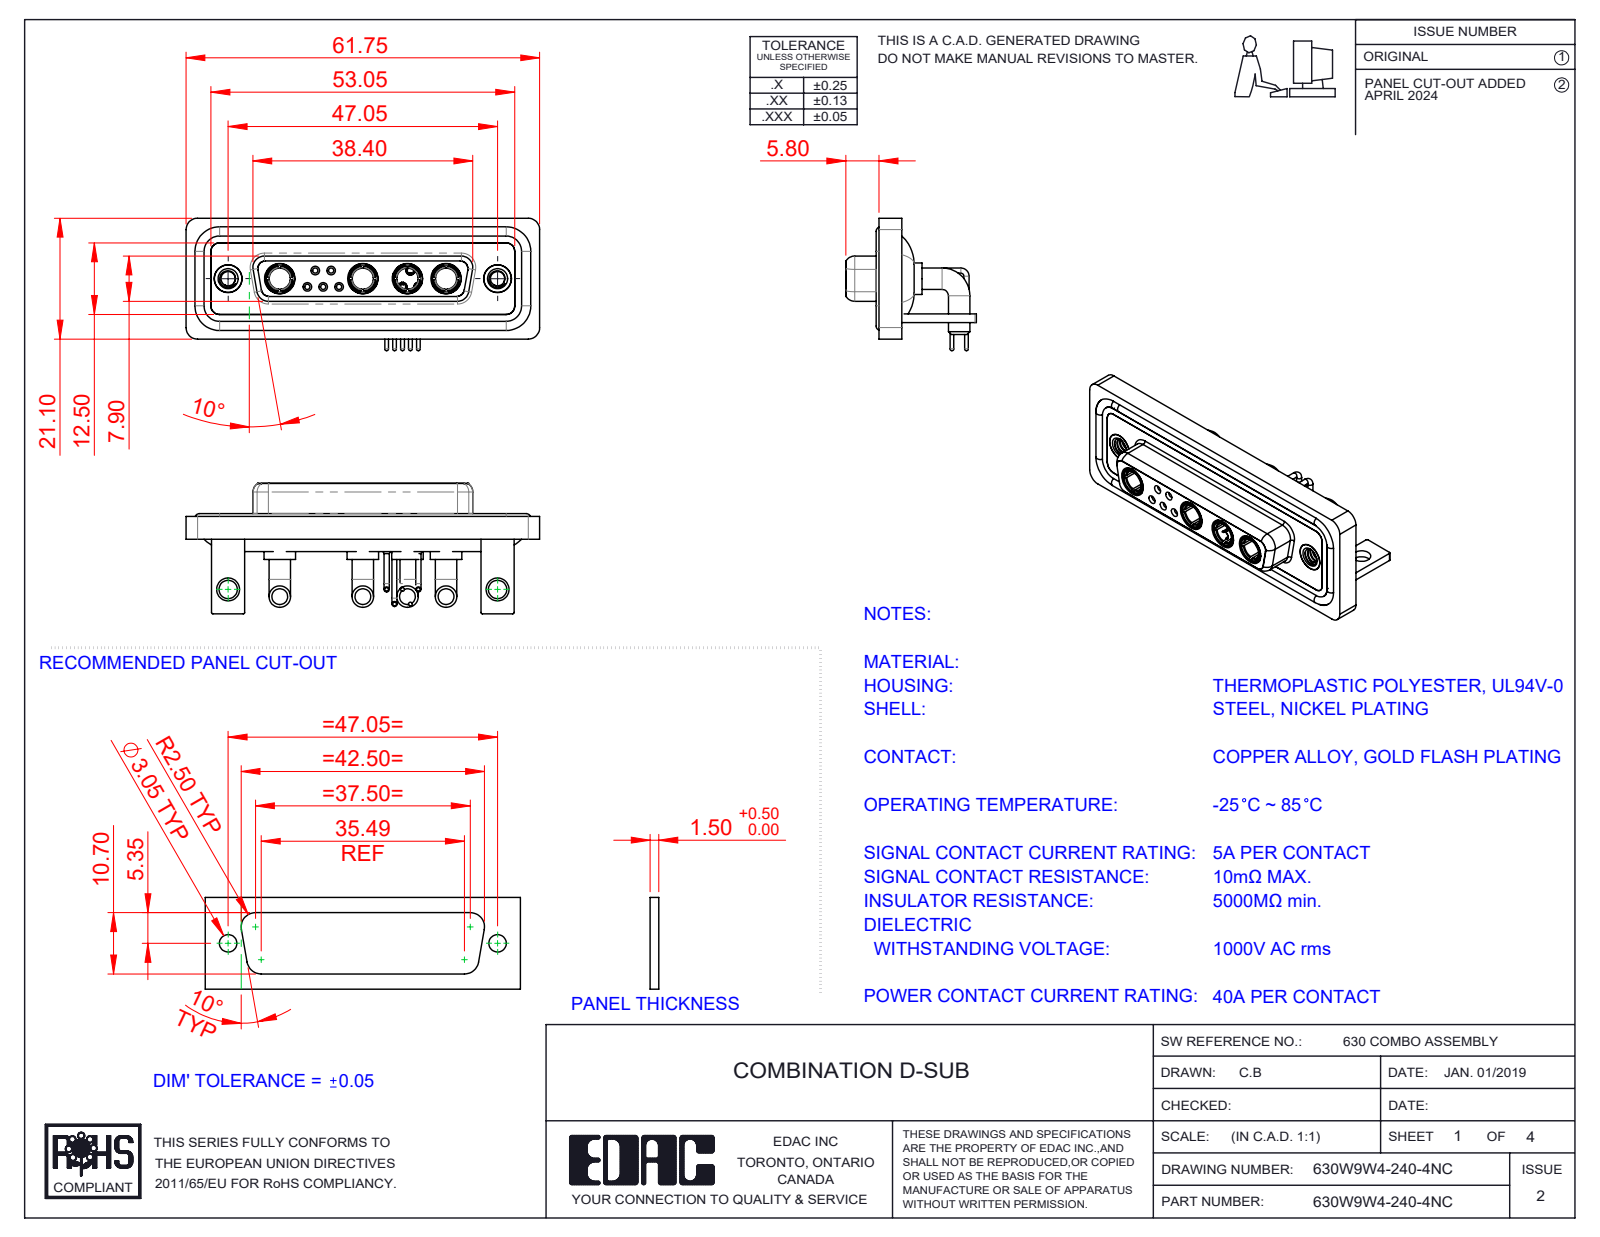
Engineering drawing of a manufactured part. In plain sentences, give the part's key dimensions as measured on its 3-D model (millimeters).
The part is named "630Combo Housing_9W4; 630Combo Stabilizer Bracket_50 Contacts; 630Combo Contact Row 1_50 Contacts; Power Socket_40A RA (+6 more)". Its 3-D file was written by "SolidWorks 2023 (CONFIG_CONTROL_DESIGN)". It is 22 solids with 1005 faces: 316 planar, 425 cylindrical and 264 other. Overall it measures 61.75 by 23.12 by 22.8 millimeters. Its volume is 9 102 cubic millimeters and its surface area 14 961 square millimeters. Round holes: 6 of diameter 4.85, 5 of diameter 0.9, 5 of diameter 1.1, 5 of diameter 1.5, 5 of diameter 2, 4 of diameter 3.7, 4 of diameter 5.3, 3 of diameter 1.6, 2 of diameter 1.7, 2 of diameter 2.5, 2 of diameter 3.2, 2 of diameter 4. Round bosses or shafts: 10 of diameter 0.9, 9 of diameter 1.6, 8 of diameter 3.75, 5 of diameter 2, 5 of diameter 1.5, 5 of diameter 0.65, 4 of diameter 5.5, 4 of diameter 5.2. Partial cylindrical surfaces (rounded edges, fillets, slot ends): 19 of radius 2, 18 of radius 1.5, 16 of radius 0.25, 8 of radius 1.35, 8 of radius 1.6, 5 of radius 0.5, 4 of radius 0.6, 4 of radius 0.65. The main face-to-face distances are 0.4, 1.8, 2.9, 3.7, 1.5, 4.1, 1.1, 1.4, 1.6, 2.5. The hole center spacings are 3.16, 2.77, 5.04, 13.85, 11.08, 12.79, 15.5, 5.54.
